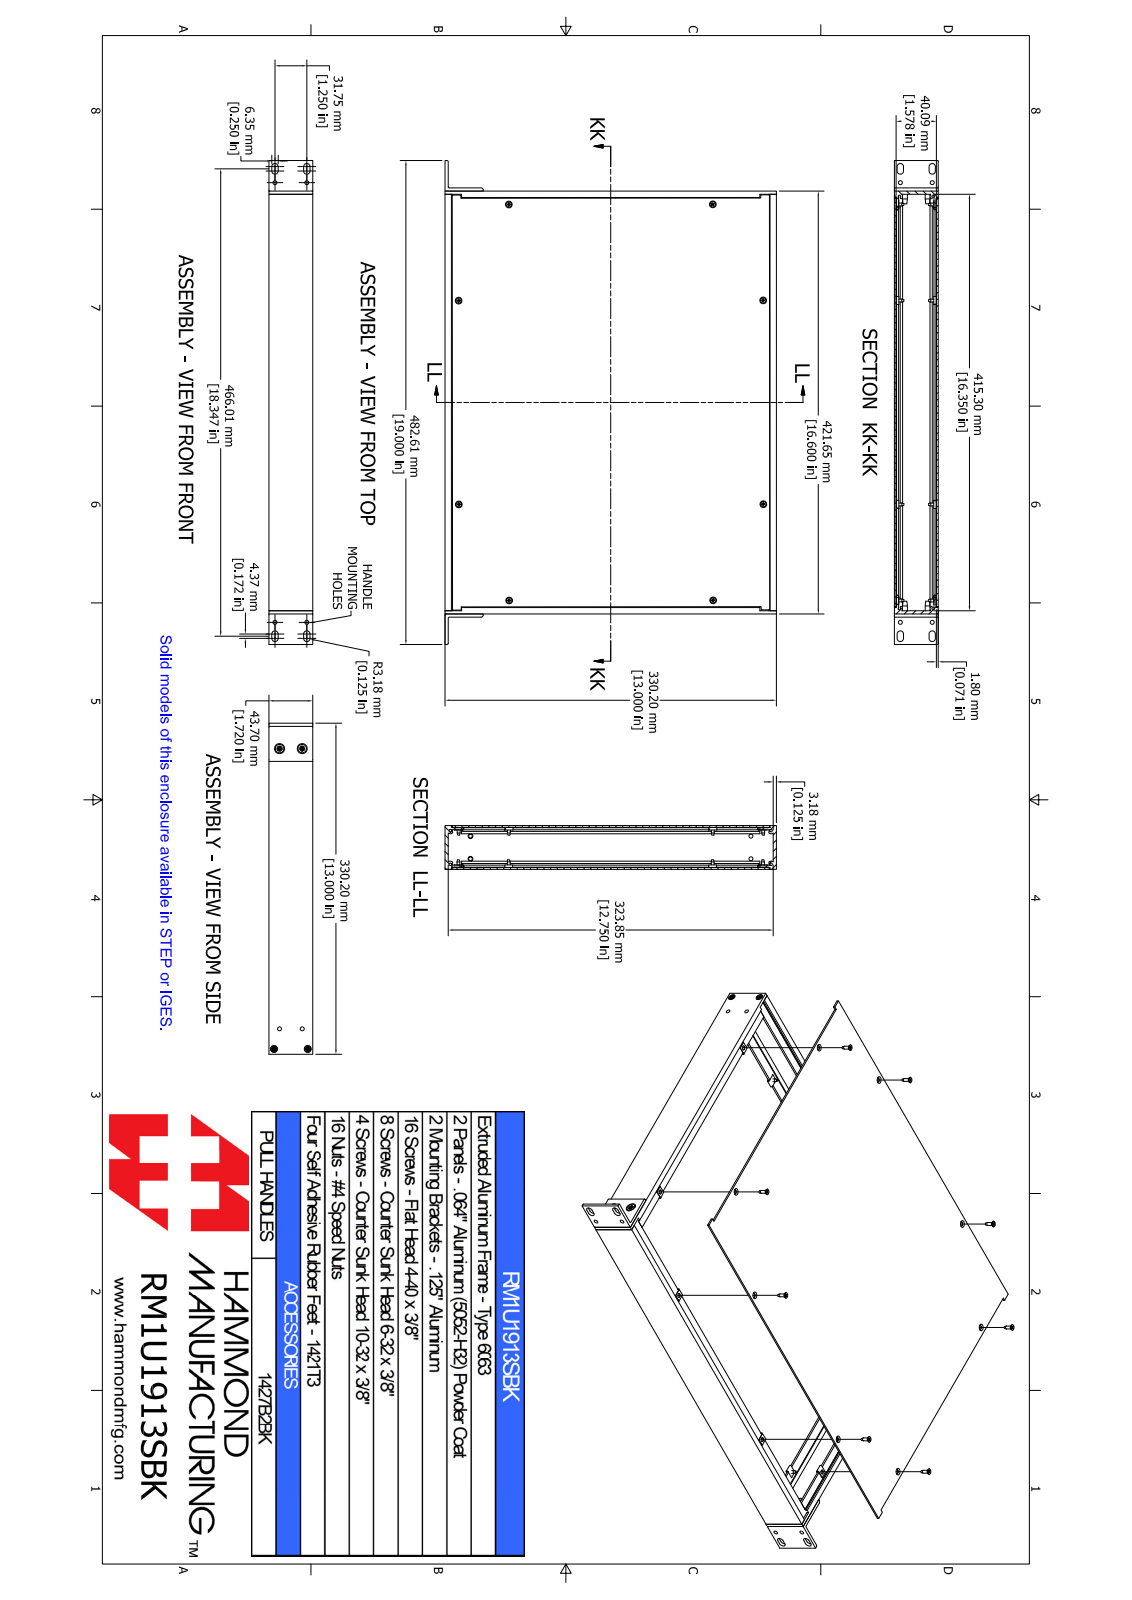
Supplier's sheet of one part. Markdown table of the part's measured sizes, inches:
| quantity | value |
| --- | --- |
| part name | RM1U1913SBK |
| STEP written by | SolidWorks 2021 (AUTOMOTIVE_DESIGN) |
| units | inches |
| bodies | 52 solids, 1352 faces (636 planar, 220 cylindrical, 496 other) |
| overall size | 19 × 13 × 1.72 |
| volume | 49.73 in³ |
| surface area | 1 211 in² |
| round holes (diameter × count) | 0.177 × 16, 0.157 × 12, 0.098 × 8, 0.169 × 8, 0.156 × 4, 0.157 × 4, 0.197 × 2 |
| round bosses / shafts (diameter × count) | 0.214 × 16, 0.112 × 16, 0.238 × 4, 0.138 × 4, 0.333 × 2, 0.19 × 2 |
| partial cylindrical surfaces (radius × count) | 0.039 × 20, 0.125 × 16, 0.049 × 14, 0.05 × 8, 0.038 × 6, 0.037 × 4, 0.079 × 2 |
| main face-to-face distances | 0.071, 1.649, 1.72, 1.578, 1.482, 0.167, 1.553, 0.096, 0.125, 0.125 |
| hole center spacings | 8, 0.819, 10.662, 11.792, 11.842, 15.545, 11.937, 4.257 |
